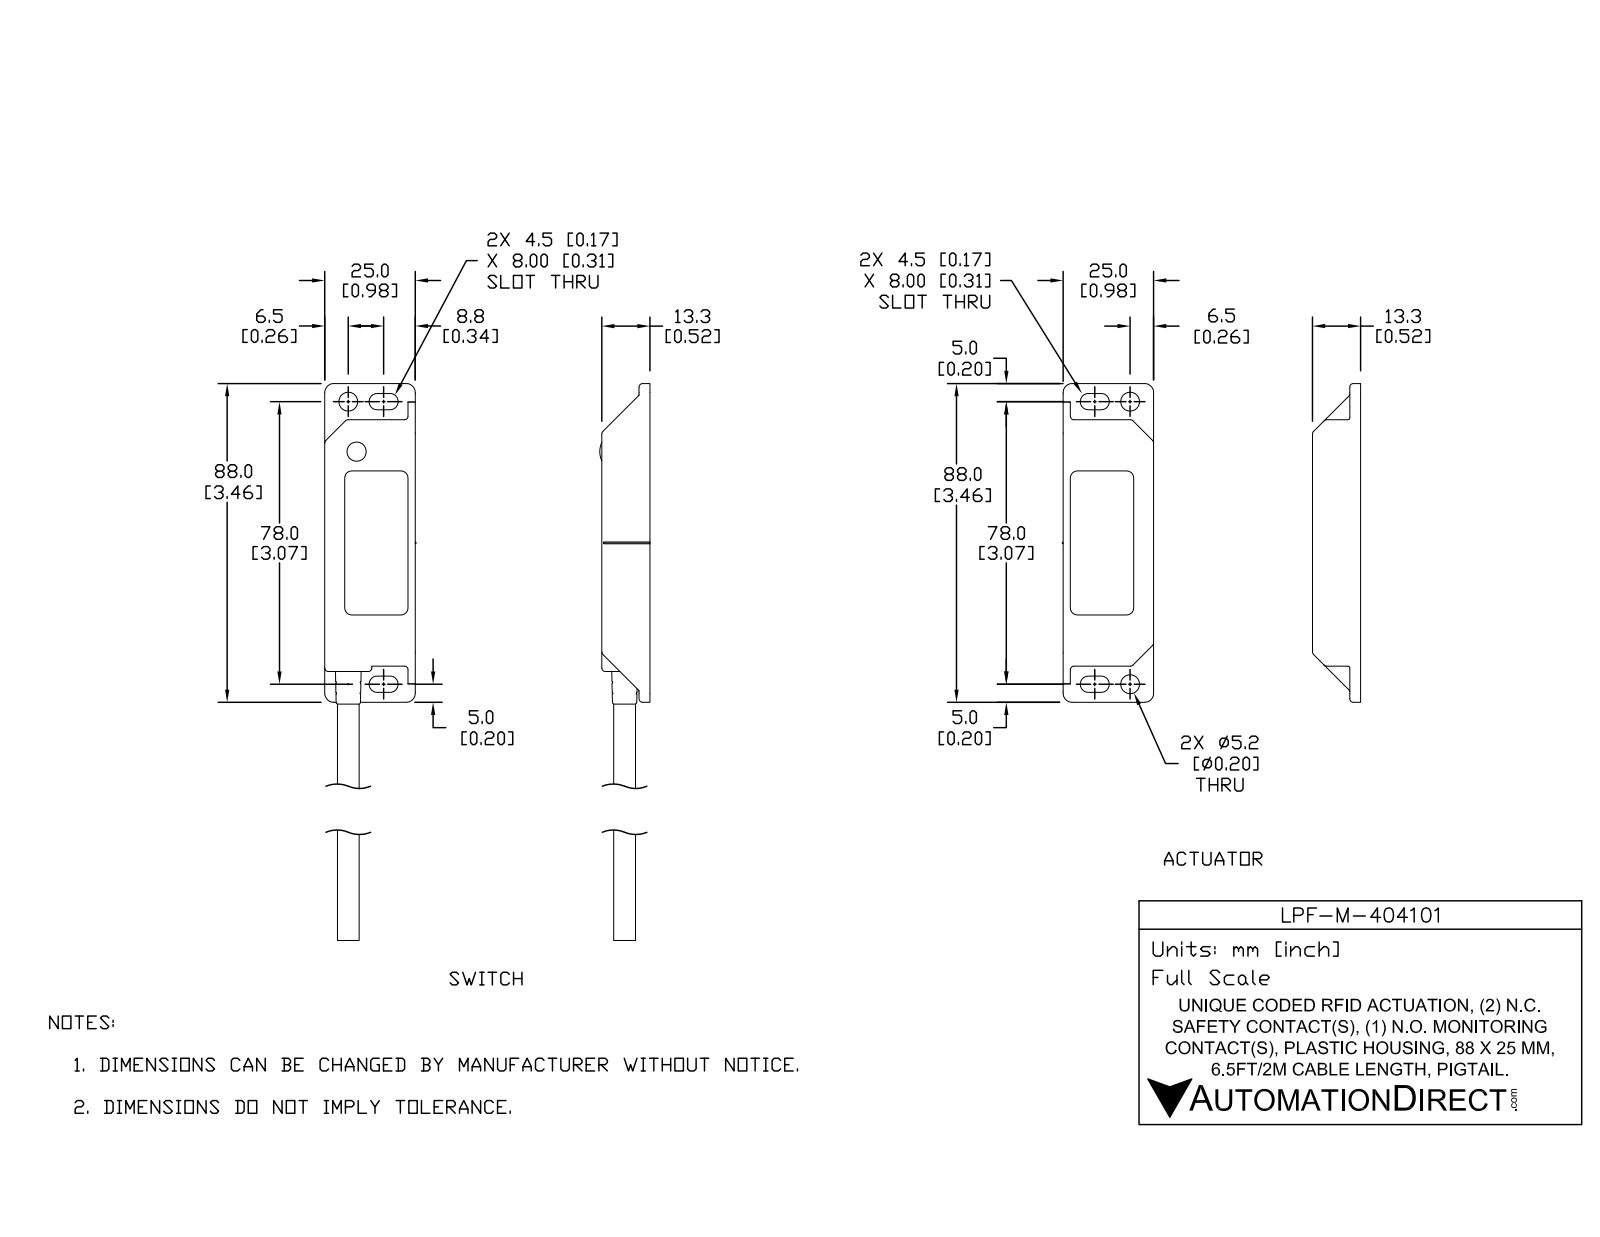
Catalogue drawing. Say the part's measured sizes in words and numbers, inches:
The part is named "LPF-M-404101_2; LPF-M-404101_1; LPF-M-404101". Its 3-D file was written by "SolidWorks 2017 (AUTOMOTIVE_DESIGN)". It is 11 solids with 1058 faces: 401 planar, 303 cylindrical and 354 other. Overall it measures 8.849 by 1.992 by 0.543 inches. Its volume is 1.638 cubic inches and its surface area 46.88 square inches. Round holes: 4 of diameter 0.197, 4 of diameter 0.205, 1 of diameter 0.119, 1 of diameter 0.173, 1 of diameter 0.213, 1 of diameter 0.232, 1 of diameter 0.276. Round bosses or shafts: 4 of diameter 0.079, 2 of diameter 0.193, 2 of diameter 0.091, 1 of diameter 0.339, 1 of diameter 0.299, 1 of diameter 0.28, 1 of diameter 0.236, 1 of diameter 0.209. Partial cylindrical surfaces (rounded edges, fillets, slot ends): 116 of radius 0.02, 49 of radius 0.039, 10 of radius 0.079, 8 of radius 0.089, 8 of radius 0.098, 6 of radius 0.012, 1 of radius 0.189. The main face-to-face distances are 0.067, 0.441, 0.079, 0.374, 0.059, 0.071, 0.508, 0.445, 0.512, 0.988. The hole center spacings are 0.748, 1.097, 1.19, 1.275, 1.48, 1.571, 1.784, 1.895.
